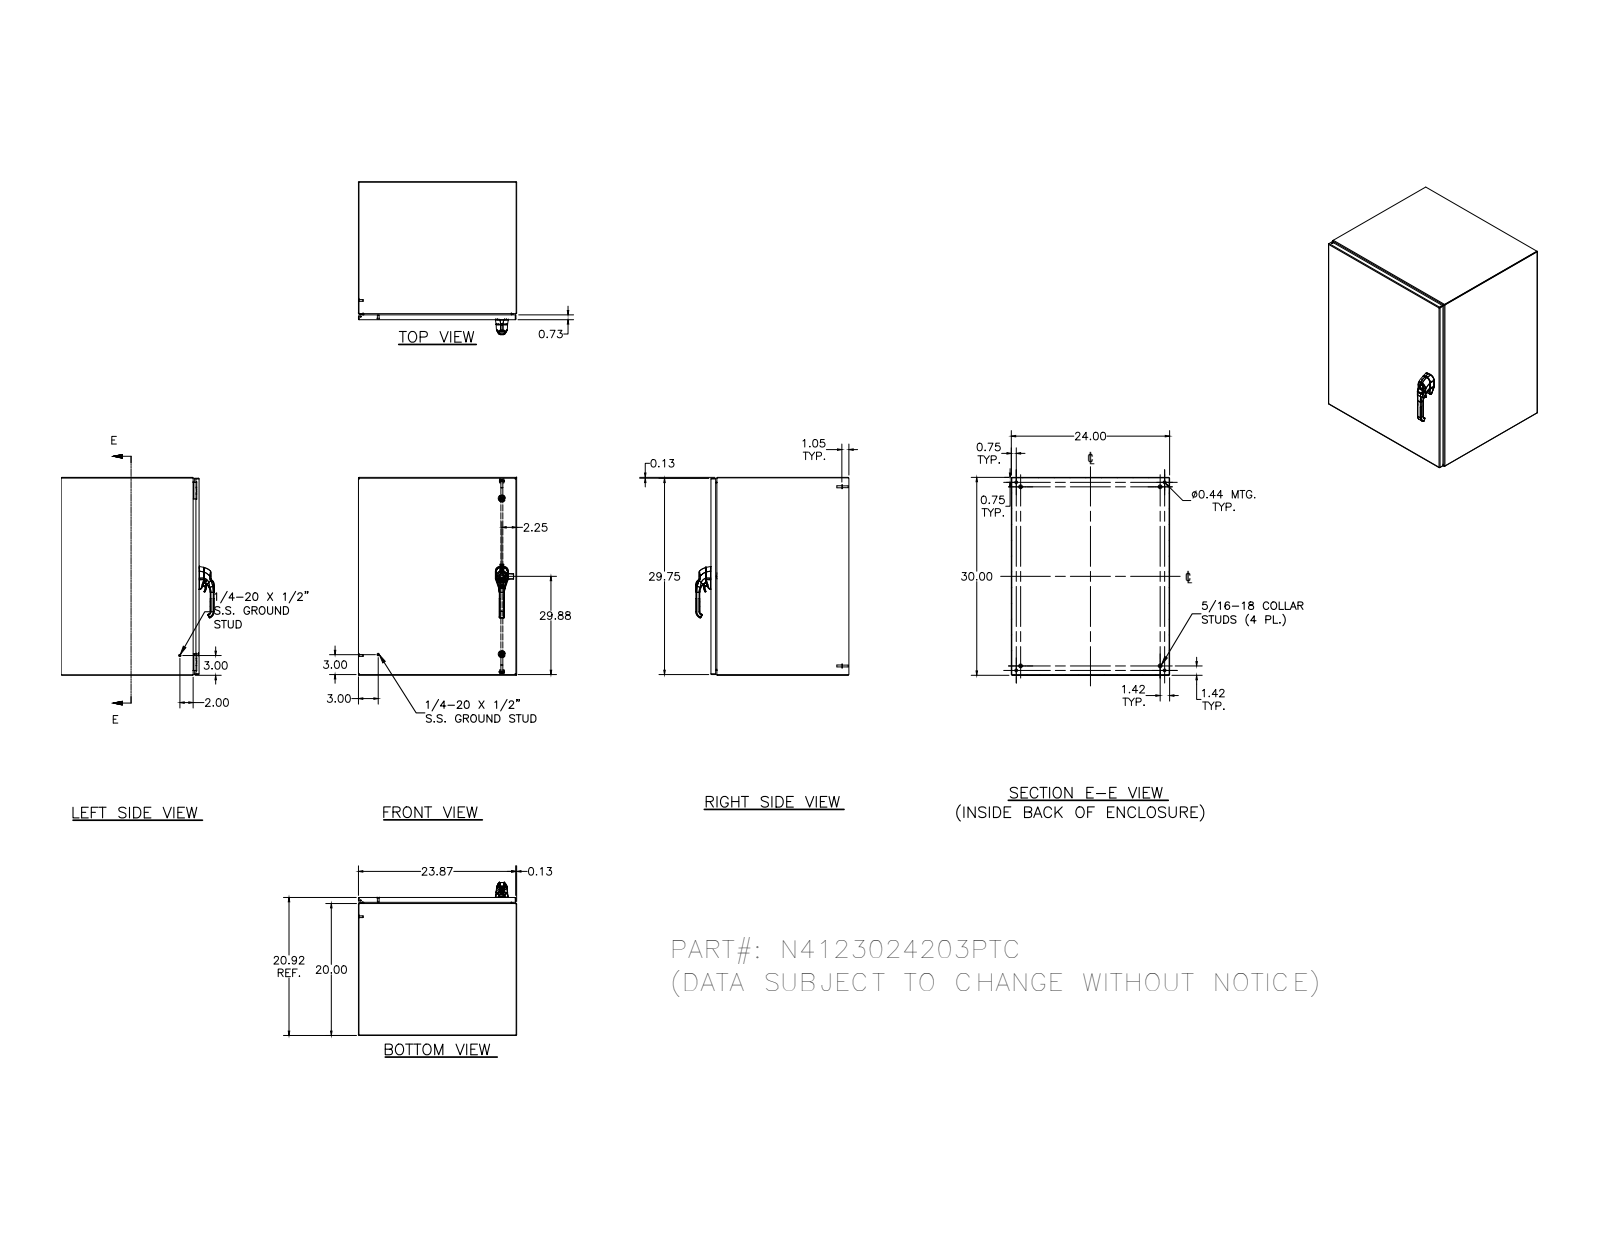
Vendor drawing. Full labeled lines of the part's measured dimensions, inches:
Part name (STEP PRODUCT): N4123024203PTC; N4123024203PTCBLR; N41224203PTCTB; HFW328176 (+8 more)
STEP written by: Autodesk Inventor 2011 (AUTOMOTIVE_DESIGN)
Units: inches
Bodies: 51 solids, 2968 faces (971 planar, 1085 cylindrical, 912 other)
Overall size (bounding box): 30 × 24 × 23.186
Volume: 284.9 in³ · Surface area: 7 790 in²
Round holes (diameter × count): ⌀0.188 ×5, ⌀0.093 ×4, ⌀0.152 ×4, ⌀0.165 ×4, ⌀0.167 ×4, ⌀0.172 ×4, ⌀0.197 ×4, ⌀0.438 ×4, ⌀0.213 ×3, ⌀0.236 ×3, ⌀0.354 ×3, ⌀0.106 ×2
Round bosses / shafts (diameter × count): ⌀0.25 ×10, ⌀0.563 ×4, ⌀0.36 ×4, ⌀0.32 ×4, ⌀0.3 ×4, ⌀0.275 ×4, ⌀0.256 ×4, ⌀0.236 ×4
Partial cylindrical surfaces — rounded edges, fillets, slot ends (radius × count): R0.02 ×174, R0.012 ×77, R0.031 ×28, R0.118 ×28, R0.05 ×26, R0.019 ×19, R0.016 ×18, R0.105 ×18
Main face-to-face distances: 0.074, 20.843, 23.926, 29.926, 20.917, 20.769, 23.852, 24, 29.852, 30
Hole centre spacings: 26, 0.017, 0.66, 21.368, 22.869, 0.019, 0.177, 0.5
